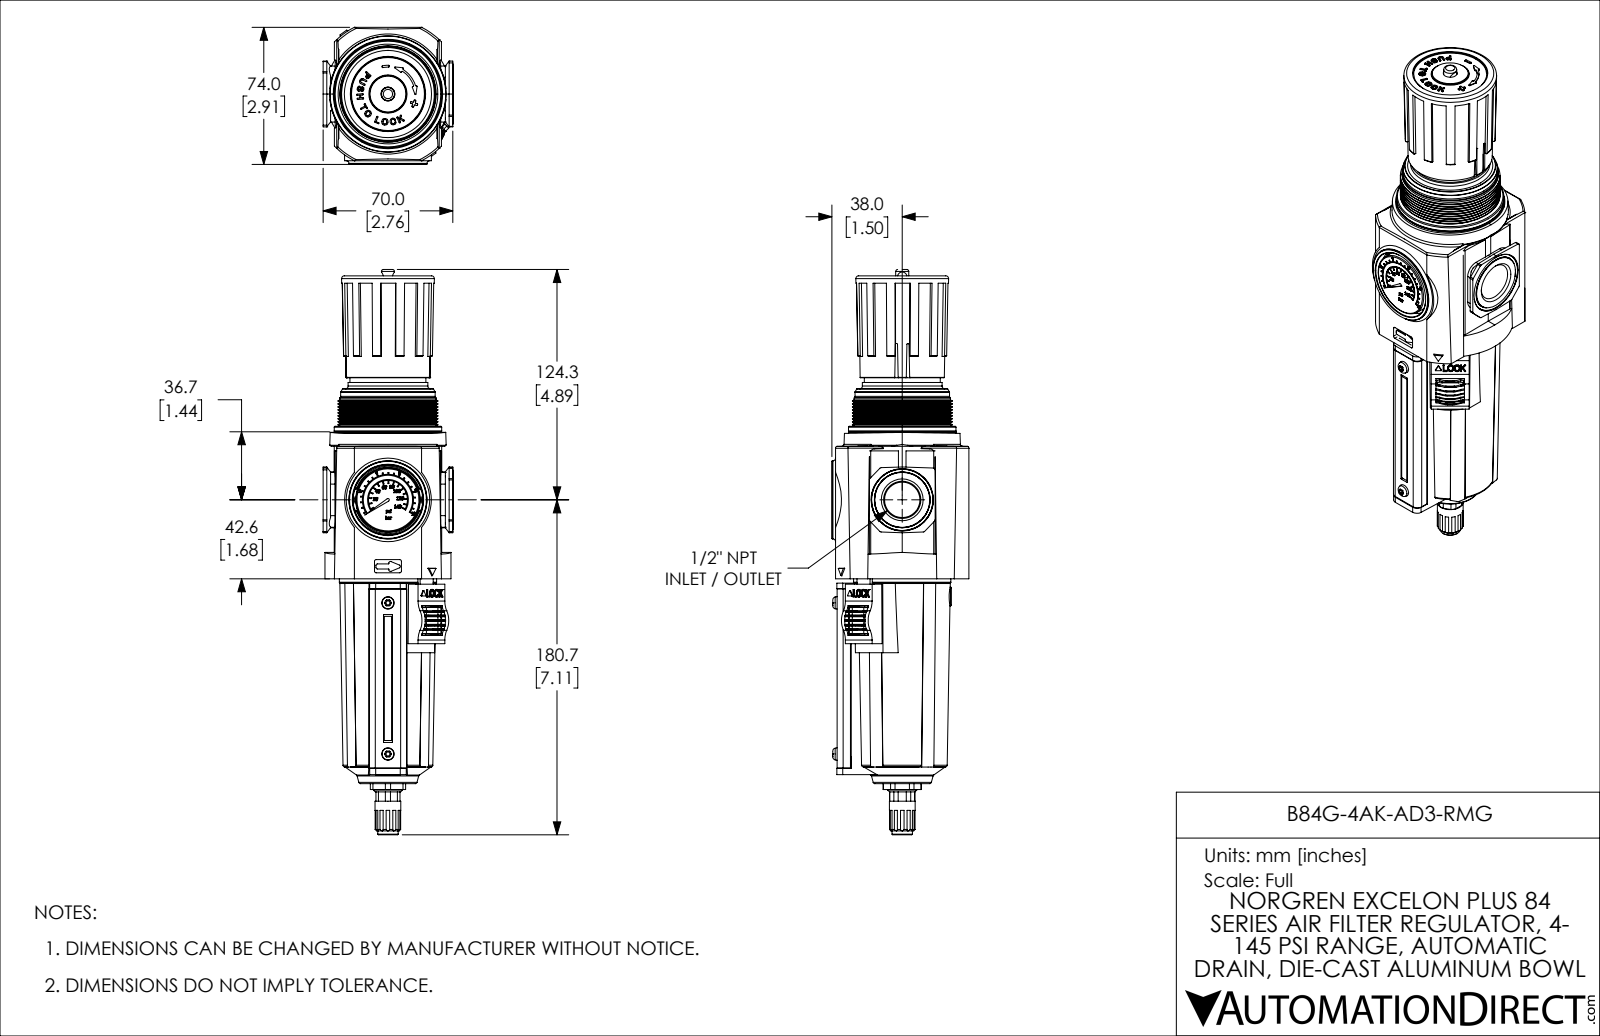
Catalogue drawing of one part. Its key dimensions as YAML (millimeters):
part_name: "B84G-4AK-AD3-RMG"
step_written_by: "SolidWorks 2021 (CONFIG_CONTROL_DESIGN)"
units: millimeters
bodies: {solids: 9, faces: 2717, planar: 1003, cylindrical: 1241, other: 473}
overall_size: [304.9, 74, 70.3]
volume: 762500
surface_area: 145600
round_holes:
  - {diameter: 2.8, count: 2}
  - {diameter: 4.5, count: 2}
  - {diameter: 1.5, count: 1}
  - {diameter: 5, count: 1}
  - {diameter: 5.6, count: 1}
  - {diameter: 6.2, count: 1}
  - {diameter: 16.1, count: 1}
  - {diameter: 19.7, count: 1}
  - {diameter: 33.5, count: 1}
  - {diameter: 59, count: 1}
  - {diameter: 62.5, count: 1}
round_bosses_or_shafts:
  - {diameter: 7.6, count: 2}
  - {diameter: 5.4, count: 2}
  - {diameter: 4, count: 2}
  - {diameter: 58, count: 1}
  - {diameter: 53.9, count: 1}
  - {diameter: 53.8, count: 1}
  - {diameter: 52.5, count: 1}
  - {diameter: 52, count: 1}
partial_cylinders:
  - {radius: 1, count: 48}
  - {radius: 0.7, count: 28}
  - {radius: 0.3, count: 27}
  - {radius: 0.5, count: 23}
  - {radius: 0.3, count: 18}
  - {radius: 1.2, count: 18}
  - {radius: 0.8, count: 16}
  - {radius: 0.1, count: 14}
face_to_face_distances: [69.1, 59, 62.4, 13, 9.2, 59.8, 15.8, 3.4, 53.2, 44]
hole_center_spacings: [21.7, 68.2, 130.1, 43.5, 63.6, 64.6, 128.2]
